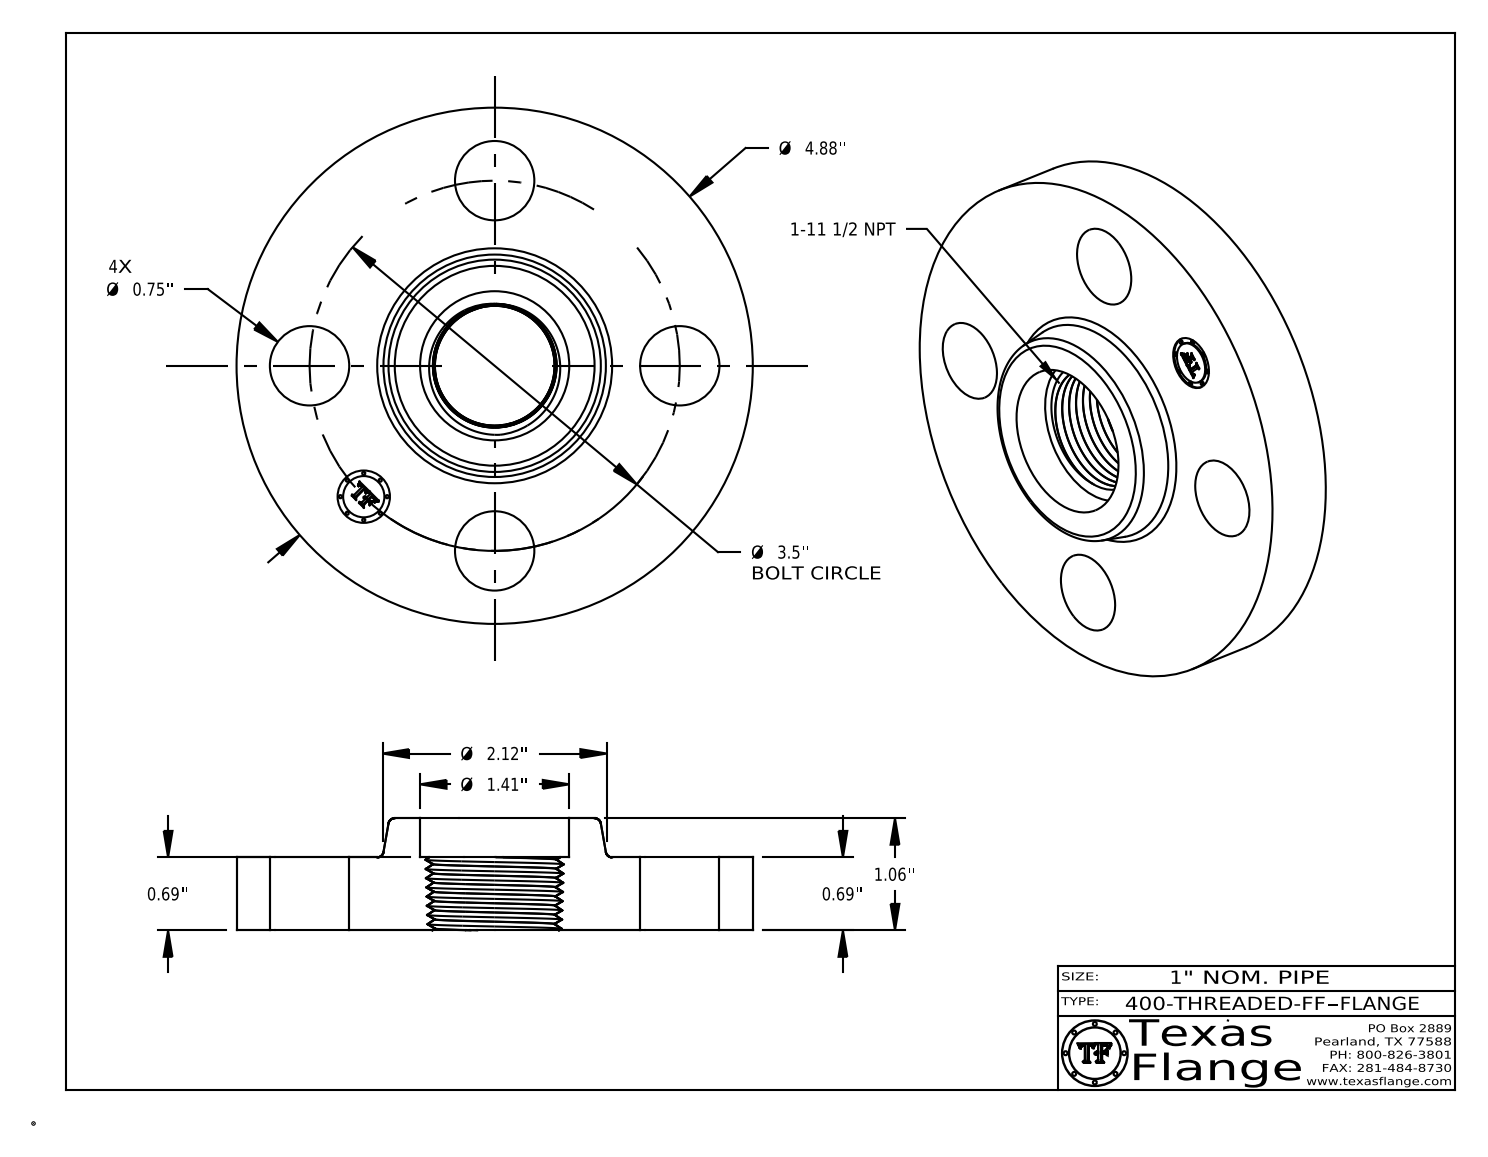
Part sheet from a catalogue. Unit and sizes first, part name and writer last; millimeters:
Units: millimetres
Overall size (bounding box): 124 × 124 × 26.9
Round holes (diameter × count): ⌀19.1 ×4, ⌀12.6 ×1, ⌀35.8 ×1
Round bosses / shafts (diameter × count): ⌀0.8 ×8, ⌀124 ×1, ⌀9.9 ×1
Main face-to-face distances: 17.5, 26.9, 9.4, 0.4, 17.1, 9.8, 3.8, 3.7, 0.7, 2.4
Hole centre spacings: 44.5, 62.9, 34, 82.1, 88.9
Volume: 188 900 mm³ · Surface area: 36 830 mm²
Bodies: 1 solid, 492 faces (369 planar, 32 cylindrical, 91 other)
Part name (STEP PRODUCT): 400-THREADED-FF
STEP written by: CATIA V5 STEP AP214 (AUTOMOTIVE_DESIGN)
